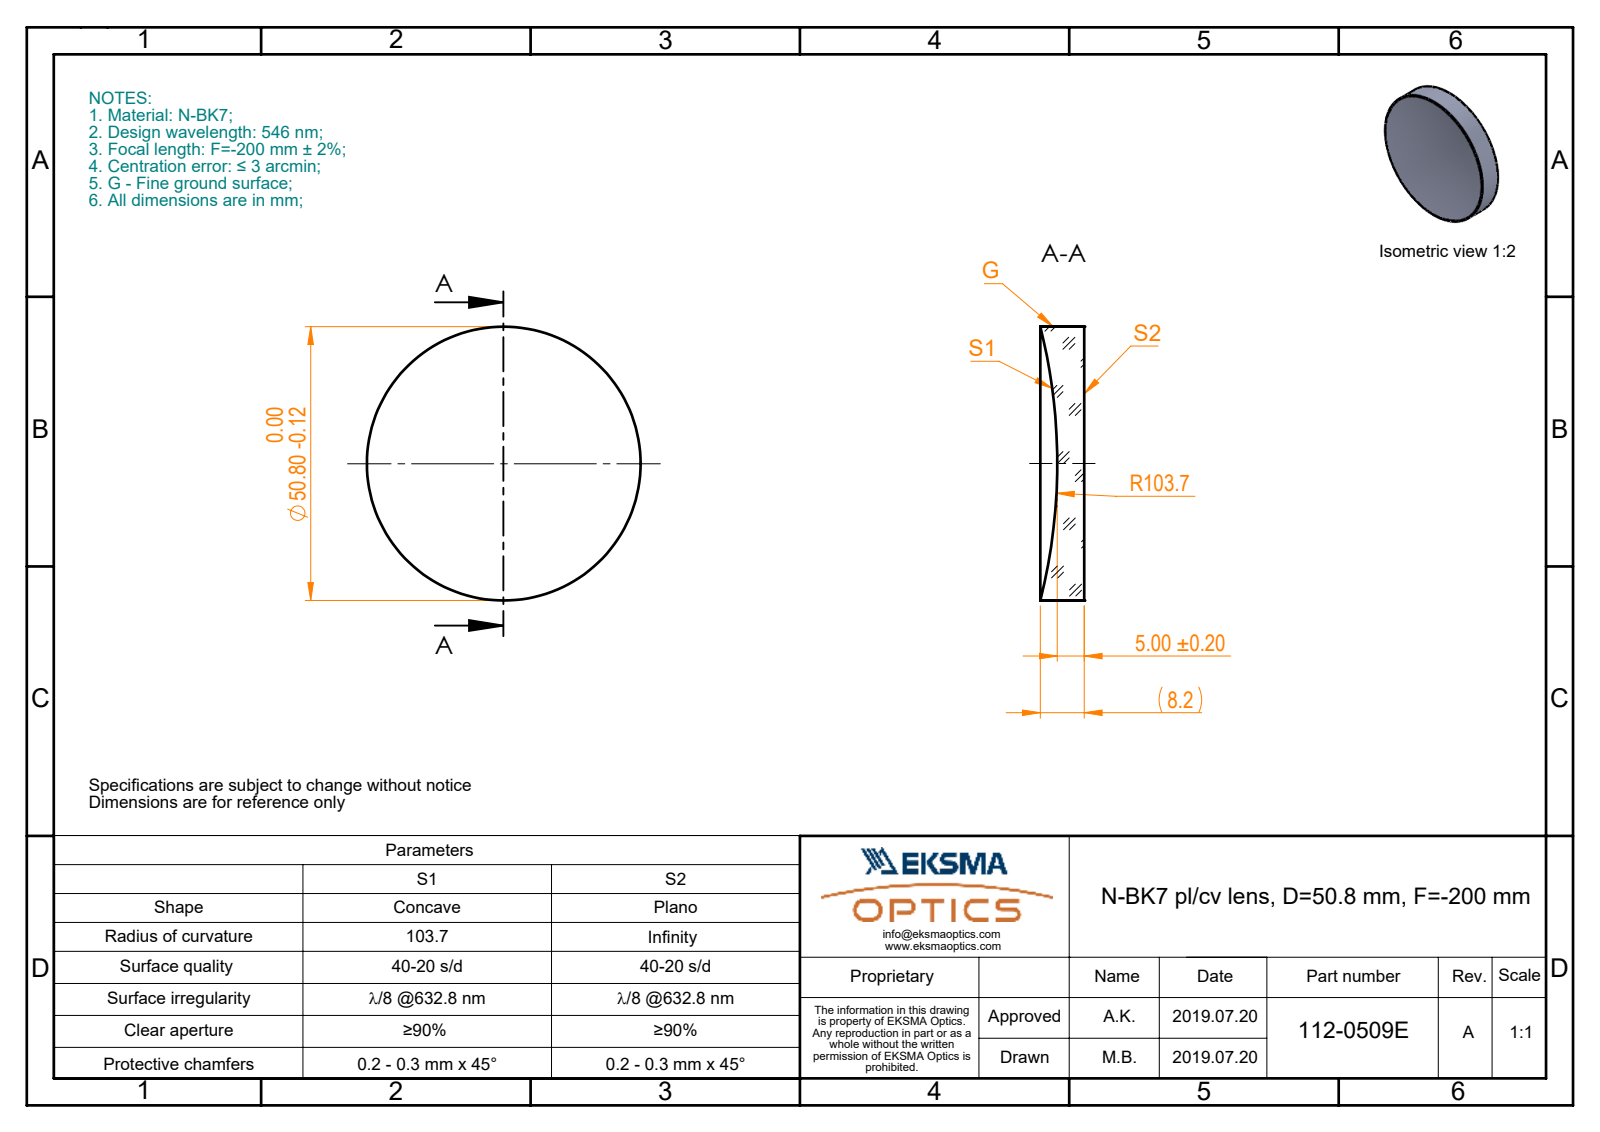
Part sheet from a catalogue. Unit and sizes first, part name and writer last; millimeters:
Units: millimetres
Overall size (bounding box): 50.8 × 50.8 × 8.16
Round bosses / shafts (diameter × count): ⌀50.8 ×1
Volume: 13 319 mm³ · Surface area: 5 387 mm²
Bodies: 1 solid, 5 faces (1 planar, 2 cylindrical, 2 other)
Part name (STEP PRODUCT): 112-0509 BK7 pl-cv 50.8 F-200
STEP written by: SolidWorks 2017 (CONFIG_CONTROL_DESIGN)
